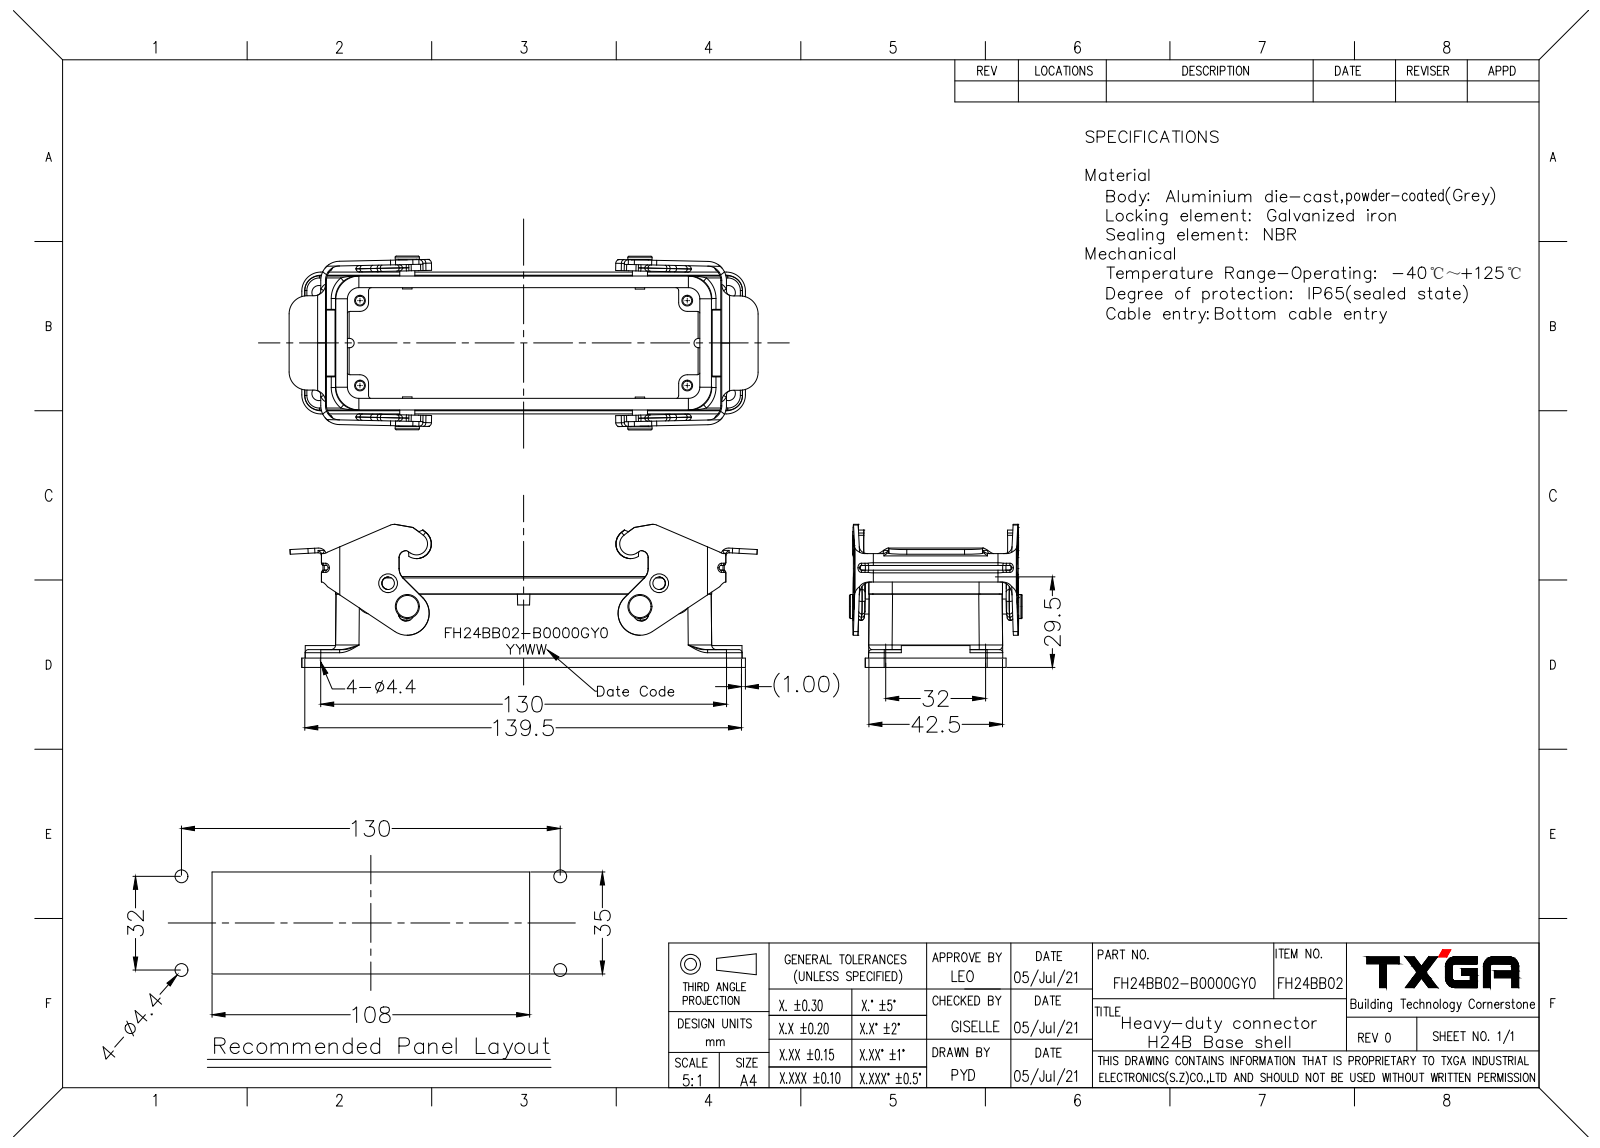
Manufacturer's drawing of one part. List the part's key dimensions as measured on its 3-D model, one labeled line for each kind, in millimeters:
Part name (STEP PRODUCT): FH24BB02-B0000GY0 H24B-BK-2L
STEP written by: SolidWorks 2021 (CONFIG_CONTROL_DESIGN)
Units: millimetres
Bodies: 1 solid, 1023 faces (281 planar, 410 cylindrical, 332 other)
Overall size (bounding box): 149.17 × 55.29 × 45.23
Volume: 44 465 mm³ · Surface area: 37 191 mm²
Round holes (diameter × count): ⌀2.84 ×4, ⌀3.4 ×4, ⌀4 ×4, ⌀4.5 ×4, ⌀2 ×2
Round bosses / shafts (diameter × count): ⌀7 ×4, ⌀5 ×4, ⌀7.7 ×2, ⌀4.8 ×2, ⌀3 ×2
Partial cylindrical surfaces — rounded edges, fillets, slot ends (radius × count): R0.99 ×112, R0.2 ×23, R2.5 ×18, R1 ×14, R0.15 ×4, R0.5 ×4, R0.65 ×4, R0.85 ×4
Main face-to-face distances: 1.5, 3.7, 52.94, 52.84, 38.9, 1.25, 4.95, 40.15, 43.85, 3
Hole centre spacings: 117.18, 120.82, 13.29, 13.3, 27, 32.09, 32.29, 32.3
